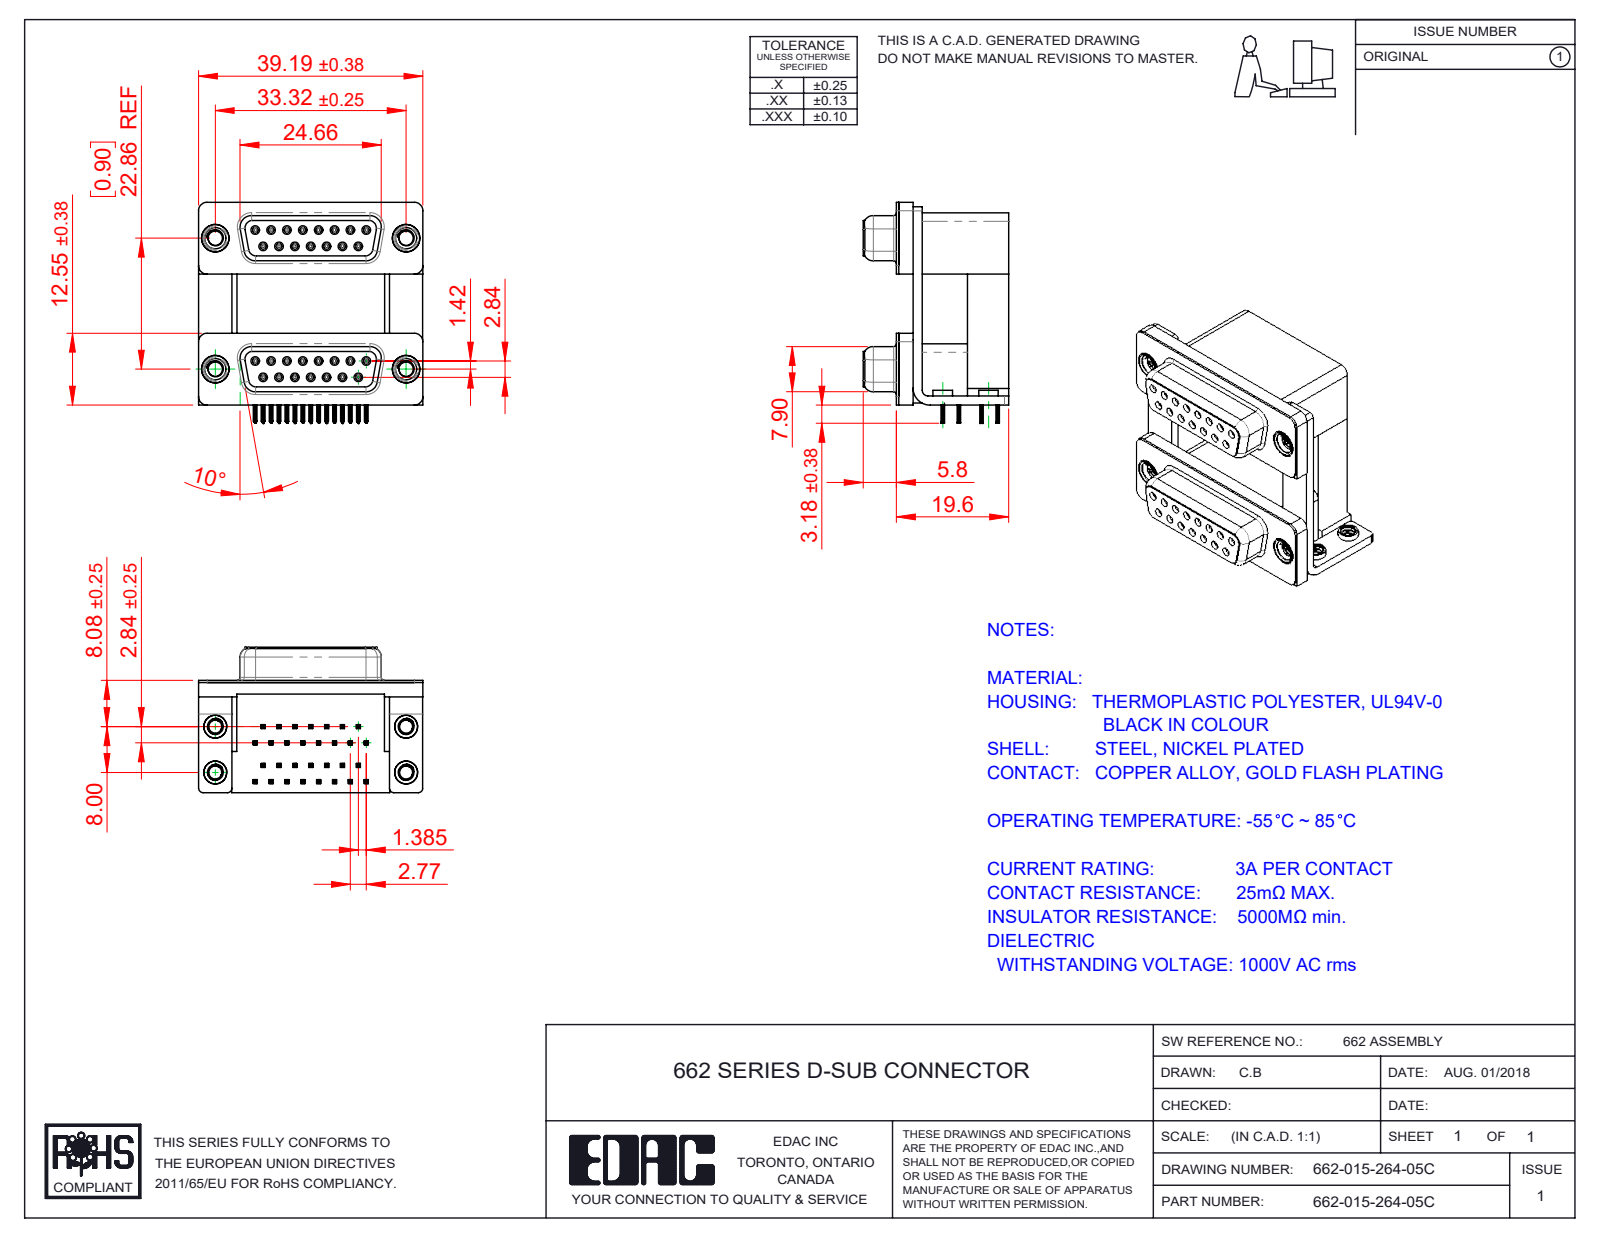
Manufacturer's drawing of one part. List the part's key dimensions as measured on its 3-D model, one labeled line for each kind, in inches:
Part name (STEP PRODUCT): 662 Shell_15 Contacts; 662 Housing Upper_15 Contacts H; 662 4-40 Threaded Board Mount; 662-015-264-05C (+8 more)
STEP written by: SolidWorks 2020 (CONFIG_CONTROL_DESIGN)
Units: inches
Bodies: 45 solids, 5006 faces (2208 planar, 1258 cylindrical, 1540 other)
Overall size (bounding box): 1.543 × 1.519 × 1
Volume: 1.025 in³ · Surface area: 29.3 in²
Round holes (diameter × count): ⌀0.031 ×30, ⌀0.035 ×30, ⌀0.089 ×4, ⌀0.098 ×4, ⌀0.108 ×4, ⌀0.126 ×4, ⌀0.138 ×4, ⌀0.157 ×4, ⌀0.189 ×4, ⌀0.197 ×4
Round bosses / shafts (diameter × count): ⌀0.047 ×30, ⌀0.193 ×4, ⌀0.187 ×4, ⌀0.157 ×4, ⌀0.154 ×4, ⌀0.134 ×4
Partial cylindrical surfaces — rounded edges, fillets, slot ends (radius × count): R0.004 ×240, R0.006 ×120, R0.014 ×60, R0.013 ×30, R0.053 ×16, R0.059 ×16, R0.011 ×14, R0.02 ×8
Main face-to-face distances: 0.756, 0.9, 0.016, 0.283, 0.472, 0.374, 0.657, 0.098, 0.421, 0.114
Hole centre spacings: 0.124, 0.907, 0.109, 0.926, 0.218, 0.327, 0.9, 0.957
